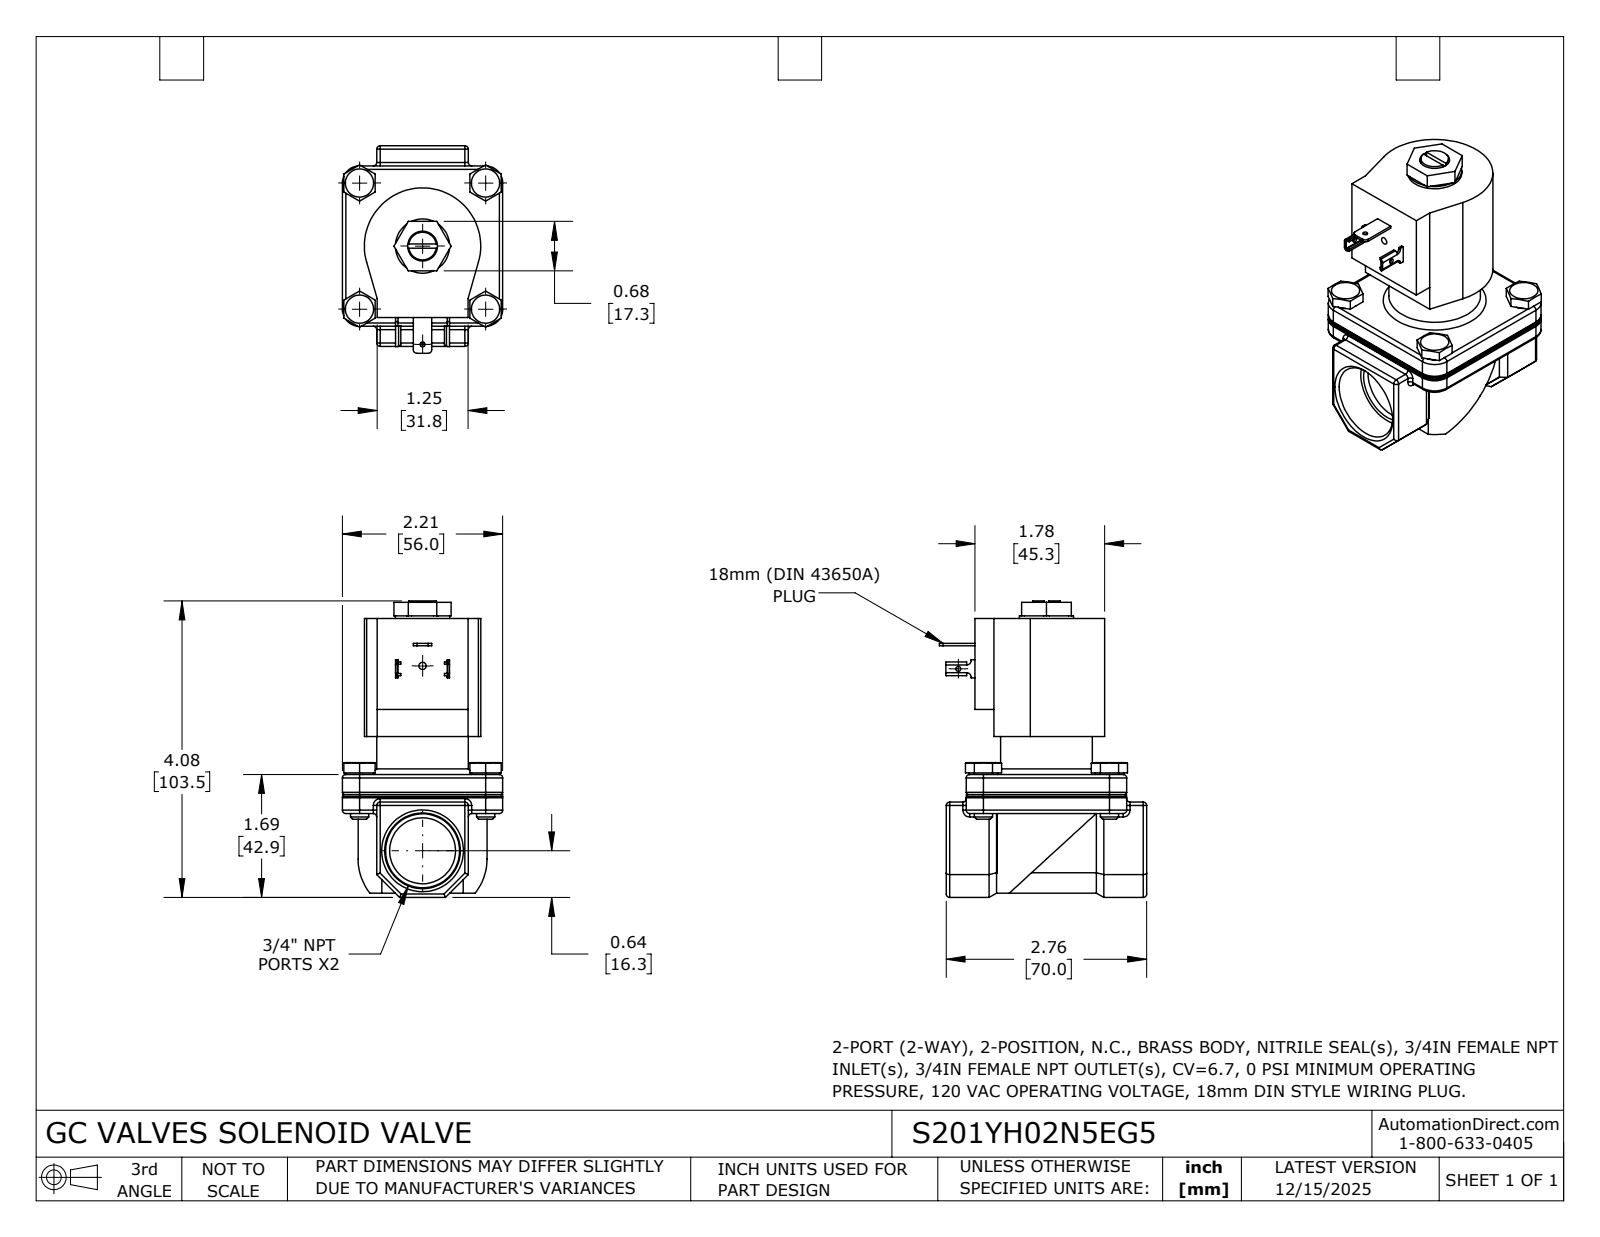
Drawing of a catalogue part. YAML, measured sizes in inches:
part_name: "S201YH02N5EG5"
step_written_by: "SolidWorks 2024 (CONFIG_CONTROL_DESIGN)"
units: inches
bodies: {solids: 1, faces: 338, planar: 166, cylindrical: 112, other: 60}
overall_size: [4.075, 2.851, 2.205]
volume: 10.16
surface_area: 43.84
round_holes:
  - {diameter: 0.066, count: 1}
  - {diameter: 0.067, count: 1}
  - {diameter: 0.1, count: 1}
  - {diameter: 0.41, count: 1}
  - {diameter: 0.906, count: 1}
round_bosses_or_shafts:
  - {diameter: 0.388, count: 4}
  - {diameter: 0.25, count: 4}
  - {diameter: 1.26, count: 1}
  - {diameter: 0.746, count: 1}
  - {diameter: 0.38, count: 1}
partial_cylinders:
  - {radius: 0.047, count: 34}
  - {radius: 0.006, count: 4}
  - {radius: 0.031, count: 4}
  - {radius: 0.041, count: 4}
  - {radius: 0.234, count: 4}
  - {radius: 0.236, count: 4}
  - {radius: 0.05, count: 2}
  - {radius: 0.06, count: 2}
face_to_face_distances: [0.059, 2.143, 0.472, 1.732, 0.537, 2.68, 2.205, 1.094, 1.631, 3.774]
hole_center_spacings: [1.35, 2.541]
